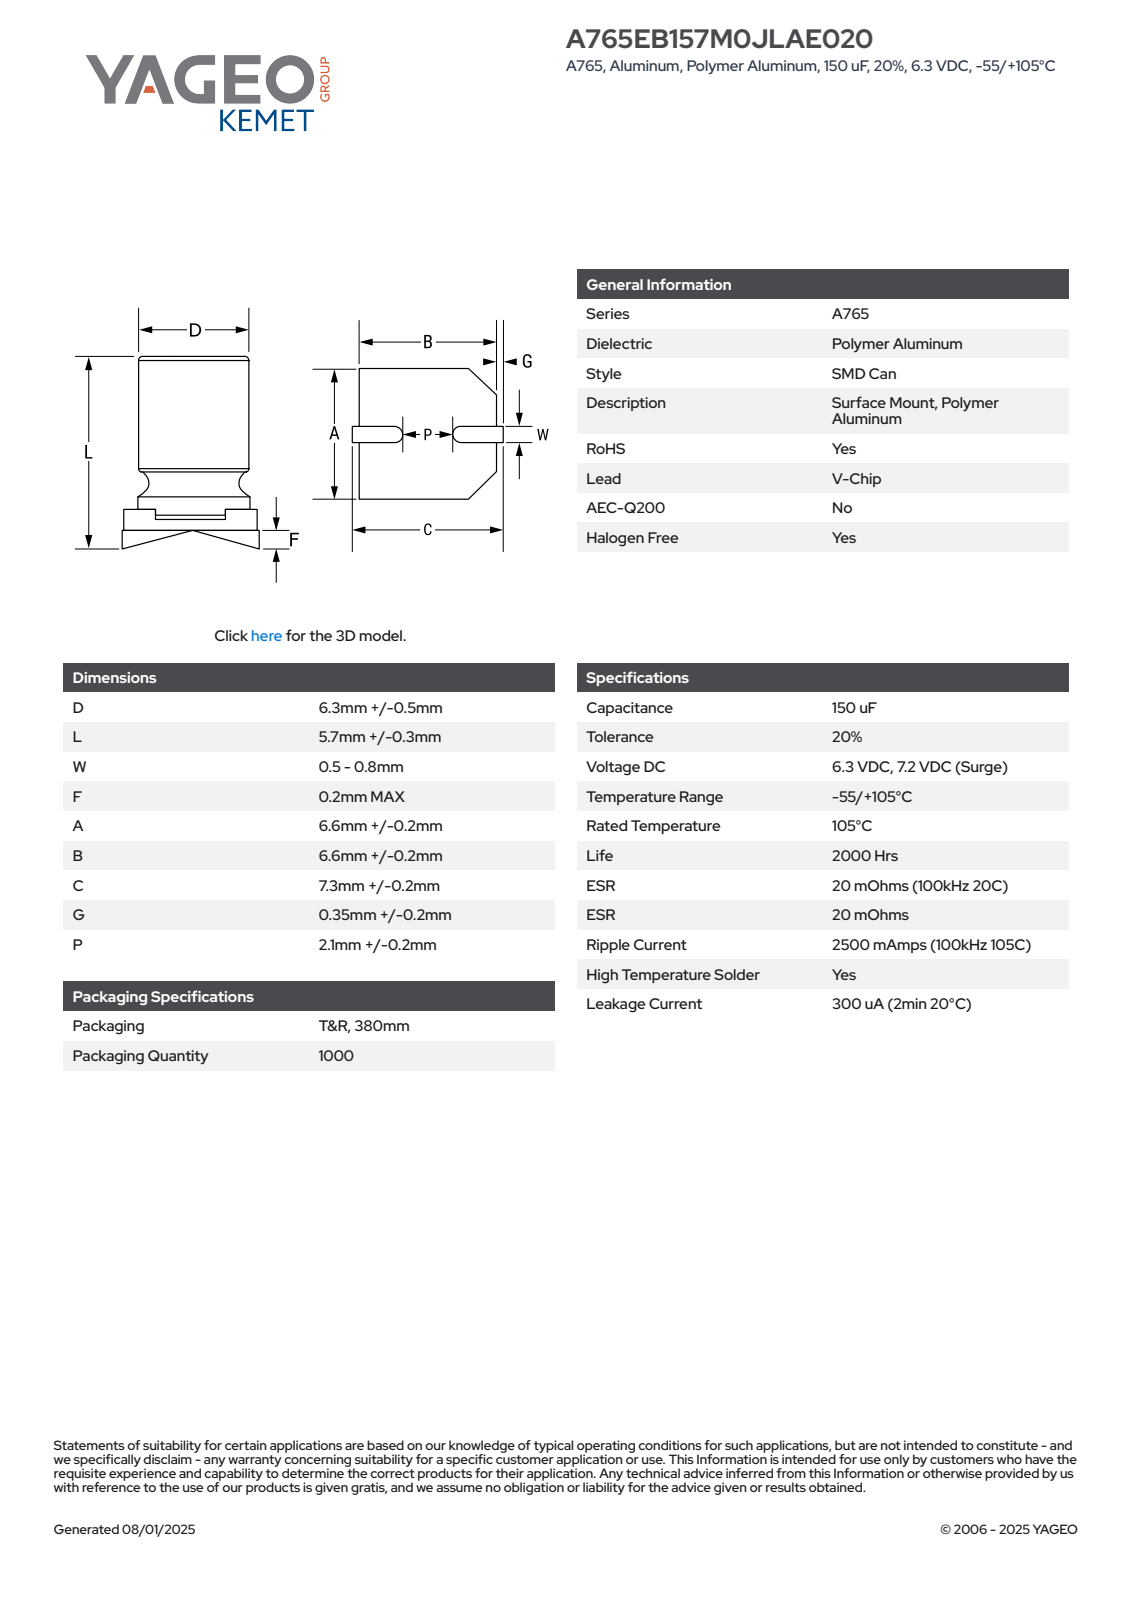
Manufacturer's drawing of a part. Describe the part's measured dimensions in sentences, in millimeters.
The part is named "CAC_KS_6.3X5.7_D6.8L6W0.8F0.2A6.8B6.8C7.5P2.3". Its 3-D file was written by "SolidWorks 2014 (AUTOMOTIVE_DESIGN)". It is 5 solids with 76 faces: 59 planar, 11 cylindrical and 6 other. Overall it measures 7.5 by 6.8 by 6 millimeters. Its volume is 201 cubic millimeters and its surface area 309 square millimeters. Round bosses or shafts: 1 of diameter 6.5. Partial cylindrical surfaces (rounded edges, fillets, slot ends): 2 of radius 0.2, 1 of radius 2.7, 1 of radius 3.4. The main face-to-face distances are 5.8, 5.5, 1.2, 6.8, 0.5, 4.8, 4.3, 1.5, 1.7, 6.
